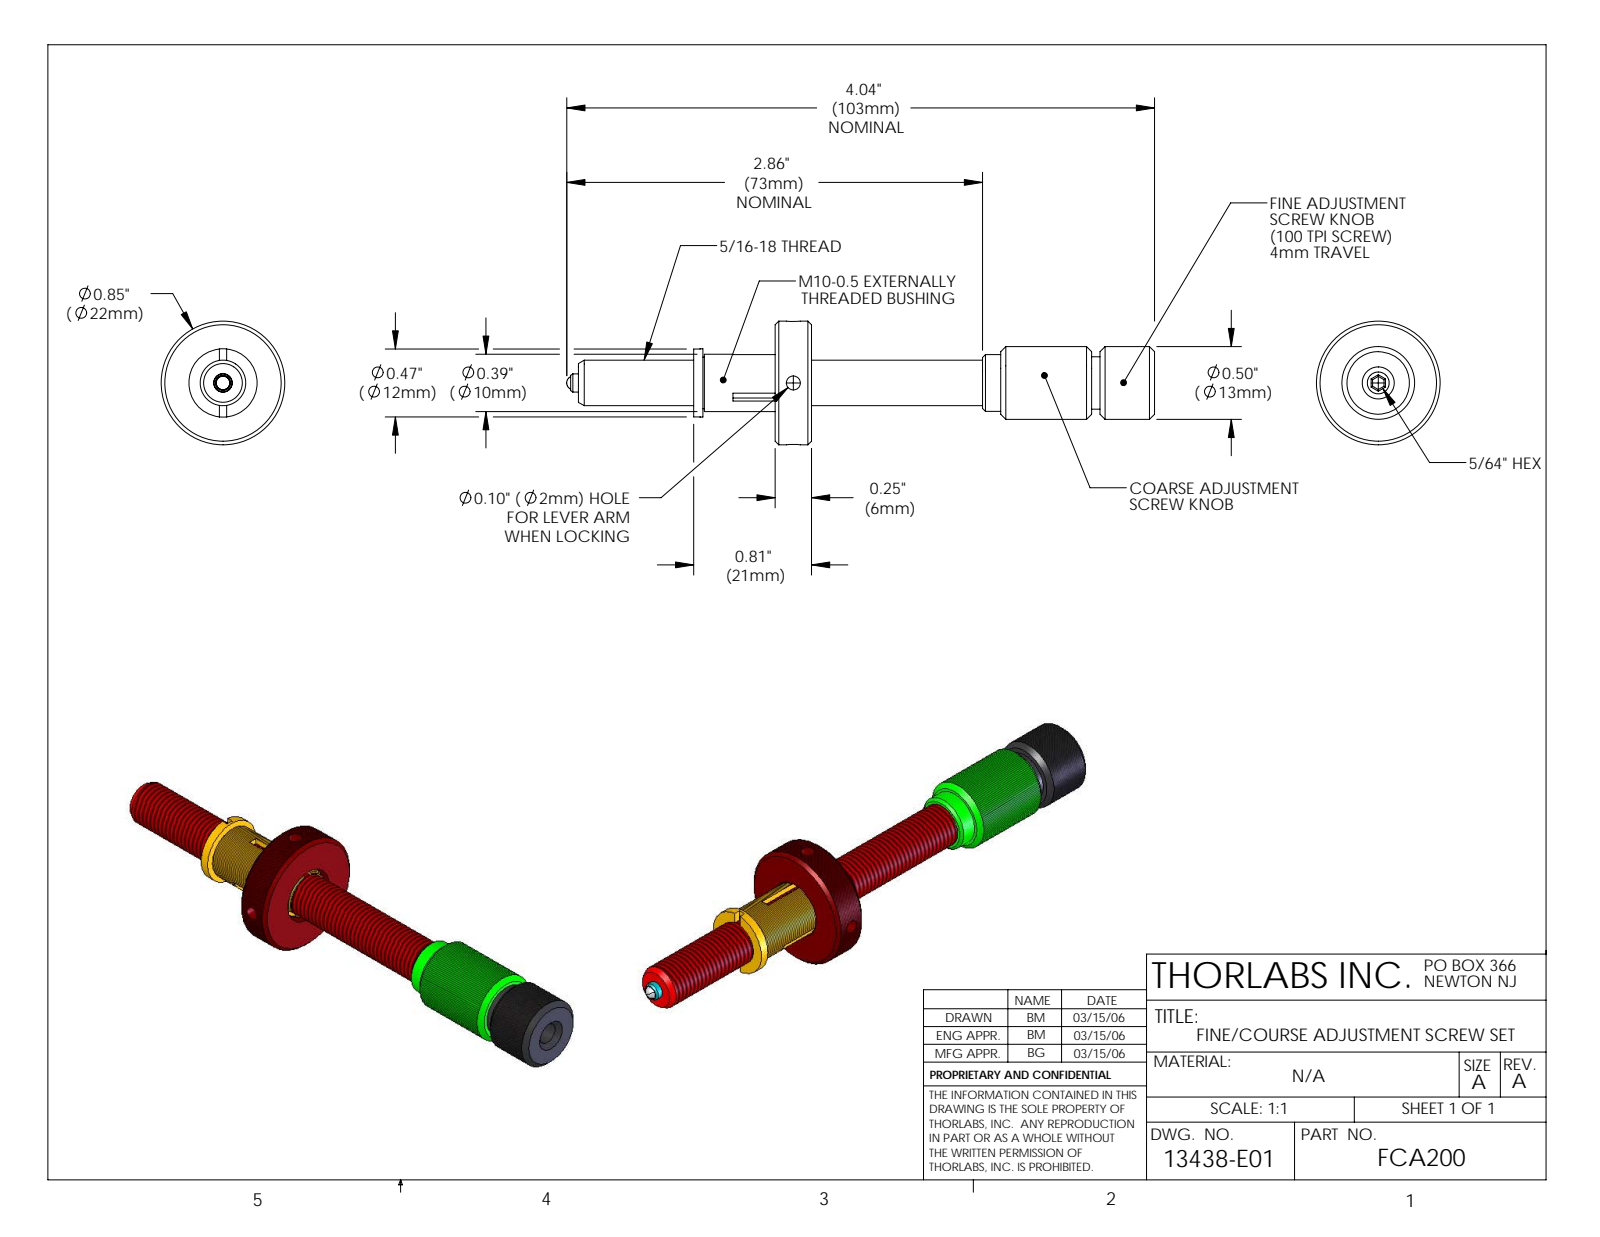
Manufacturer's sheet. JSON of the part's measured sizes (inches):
{"part_name": "13438-E0W", "step_written_by": "SolidWorks 2007 (AUTOMOTIVE_DESIGN)", "units": "inches", "bodies": {"solids": 7, "faces": 154, "planar": 50, "cylindrical": 60, "other": 44}, "overall_size": [4.041, 0.85, 0.85], "volume_in3": 0.523, "surface_area_in2": 13.09, "round_holes": [[0.096, 2], [0.094, 1], [0.126, 1], [0.136, 1], [0.15, 1], [0.187, 1], [0.194, 1], [0.227, 1], [0.313, 1], [0.38, 1], [0.394, 1], [0.4, 1]], "round_bosses_or_shafts": [[0.85, 1], [0.5, 1], [0.469, 1], [0.39, 1], [0.36, 1], [0.354, 1], [0.125, 1]], "face_to_face_distances": [0.25, 2.608, 2.358, 0.56, 0.81, 3.169, 2.55, 1.99, 1.74, 0.618]}
